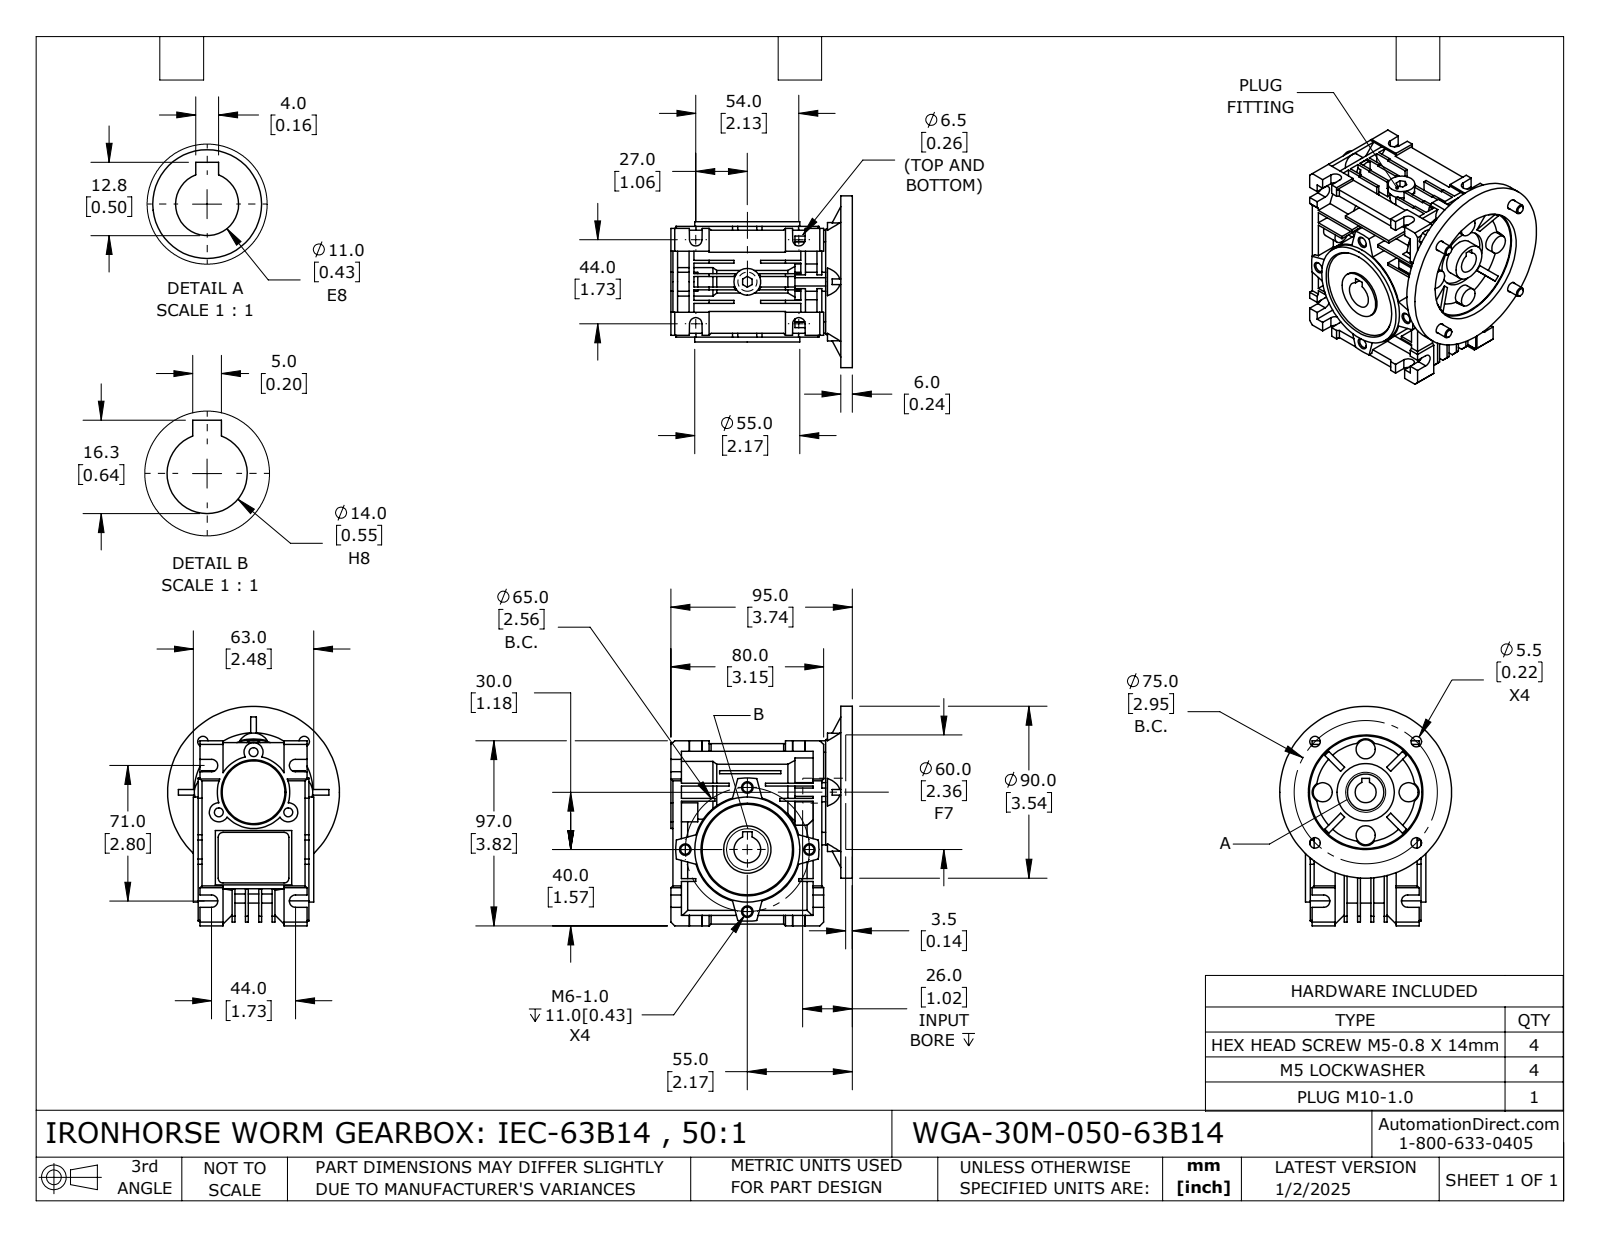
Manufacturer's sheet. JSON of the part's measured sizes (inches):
{"part_name": "WGA-30M-050-63B14", "step_written_by": "SolidWorks 2024 (CONFIG_CONTROL_DESIGN)", "units": "inches", "bodies": {"solids": 14, "faces": 905, "planar": 566, "cylindrical": 239, "other": 100}, "overall_size": [4.528, 4.004, 3.543], "volume_in3": 20.73, "surface_area_in2": 175.1, "round_holes": [[0.194, 4], [0.201, 4], [0.217, 4], [0.183, 3], [0.194, 2], [0.354, 1], [0.433, 1], [0.453, 1], [0.551, 1], [0.571, 1], [0.748, 1], [0.976, 1]], "round_bosses_or_shafts": [[0.394, 4], [0.362, 4], [0.197, 4], [3.543, 1], [2.205, 1], [2.165, 1], [1.496, 1], [1.457, 1]], "partial_cylinders_radius": [[0.128, 8], [0.098, 4], [0.217, 4], [0.335, 4], [0.197, 3], [0.295, 1], [0.669, 1], [0.846, 1]], "face_to_face_distances": [0.059, 0.276, 0.217, 0.039, 0.551, 0.177, 0.335, 0.236, 0.394, 0.079], "hole_center_spacings": [1.28, 1.476, 1.809, 2.088, 0.827, 0.711, 1.067, 1.432]}
